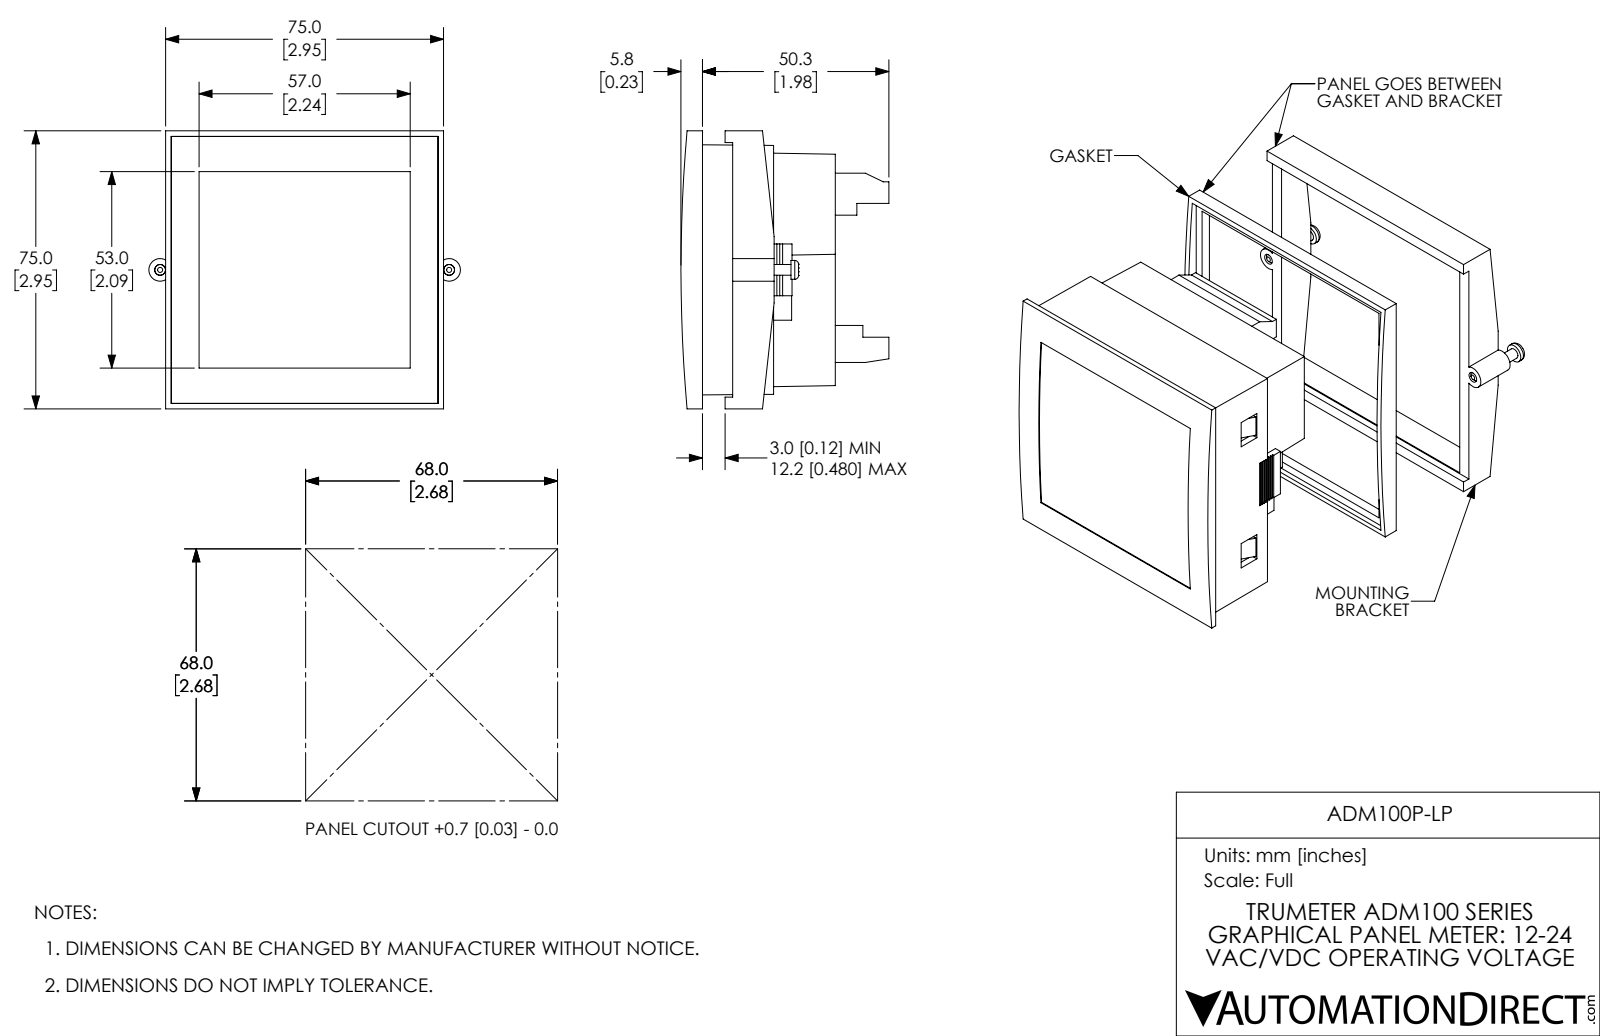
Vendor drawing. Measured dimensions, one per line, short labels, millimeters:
name: ADM100P-LP
written by: SolidWorks 2021 (CONFIG_CONTROL_DESIGN)
unit: mm
bodies: 23 solids, 419 faces (335 planar, 76 cylindrical, 8 other)
size: 84.1 × 75 × 56.1
volume: 156 700 mm³; area: 58 480 mm²
holes: 13× ⌀3.8, 2× ⌀2.9
bosses: 13× ⌀3.8, 2× ⌀5.1, 2× ⌀2.9
rounds: 2× R3, 2× R432.7
face distances: 1.9, 7.7, 6, 69, 67.5, 2.3, 3.8, 71.2, 65.6, 29
hole spacings: 42, 5.1, 42.6, 10.2, 43.8, 15.2, 45.5, 20.3
